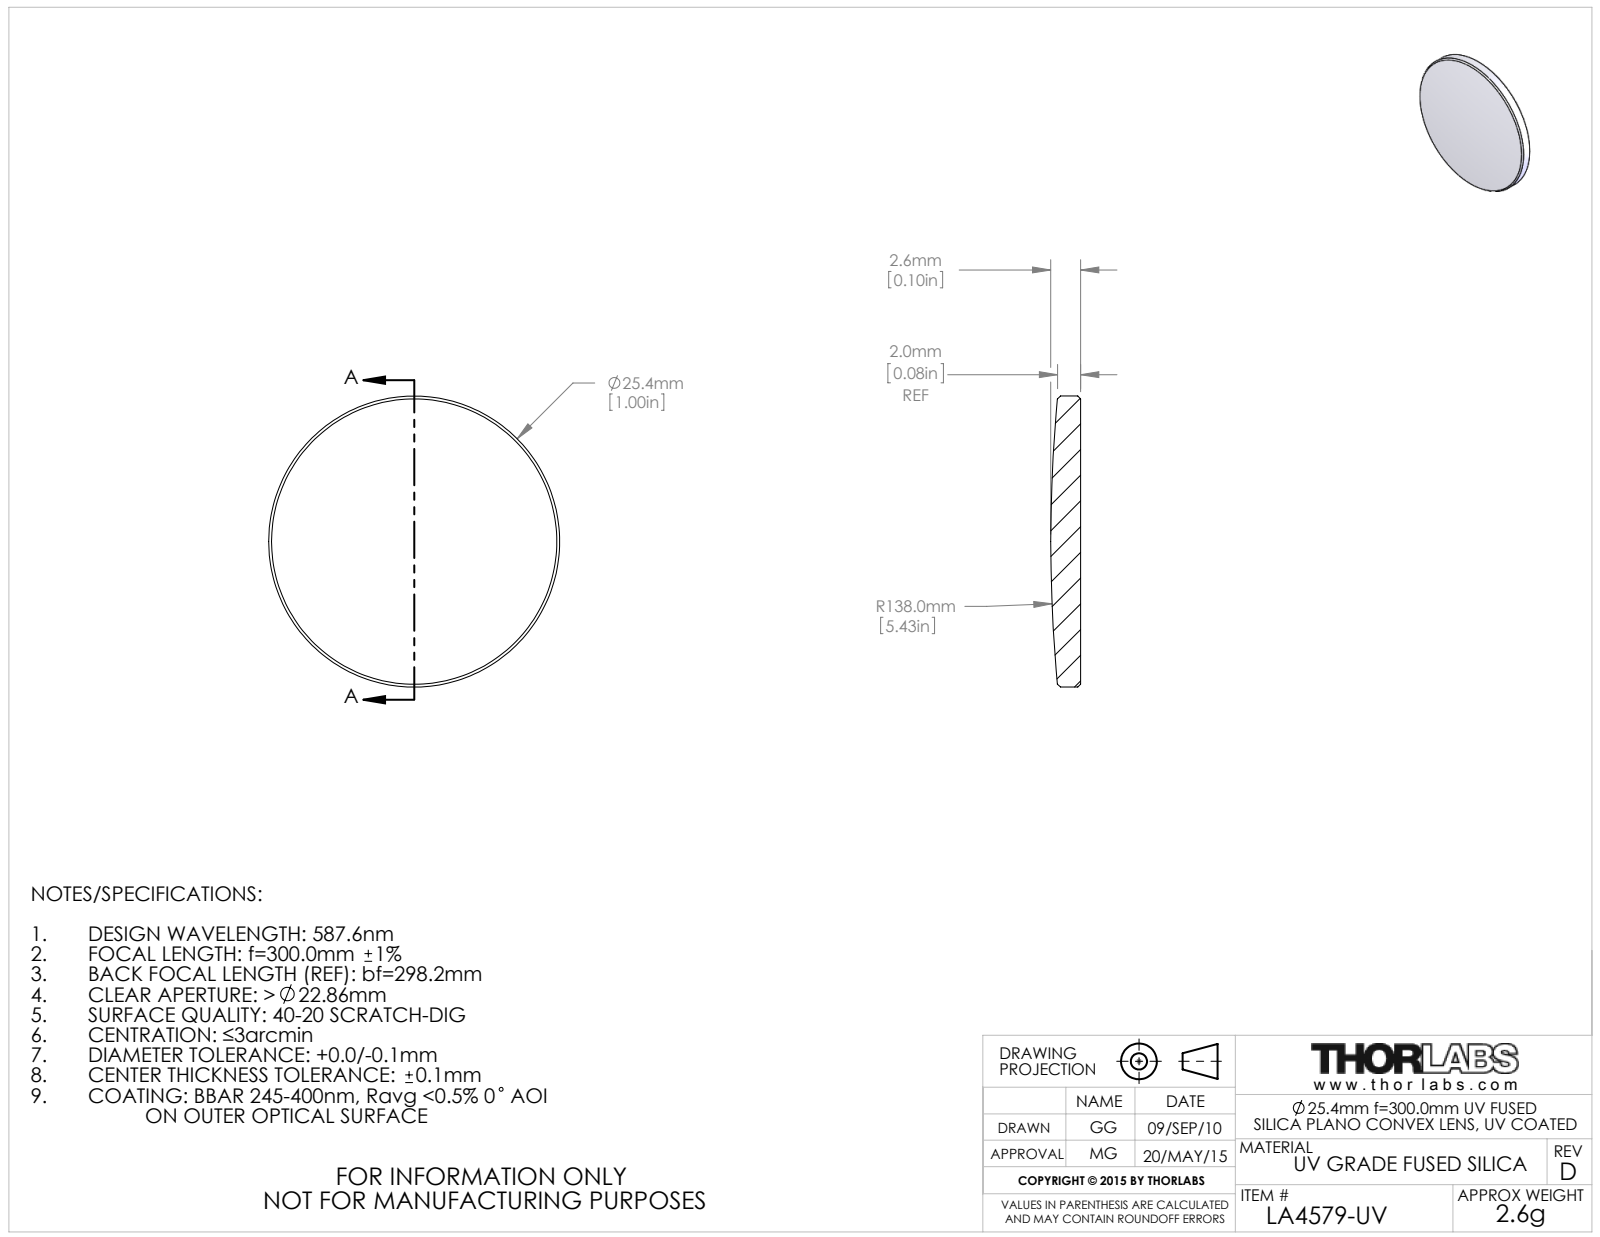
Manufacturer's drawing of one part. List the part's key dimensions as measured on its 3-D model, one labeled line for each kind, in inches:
Part name (STEP PRODUCT): 4288-E0W
STEP written by: SolidWorks 2014 (CONFIG_CONTROL_DESIGN)
Units: inches
Bodies: 1 solid, 9 faces (1 planar, 2 cylindrical, 6 other)
Overall size (bounding box): 1 × 1 × 0.102
Volume: 0.071 in³ · Surface area: 1.786 in²
Round bosses / shafts (diameter × count): ⌀1 ×1
